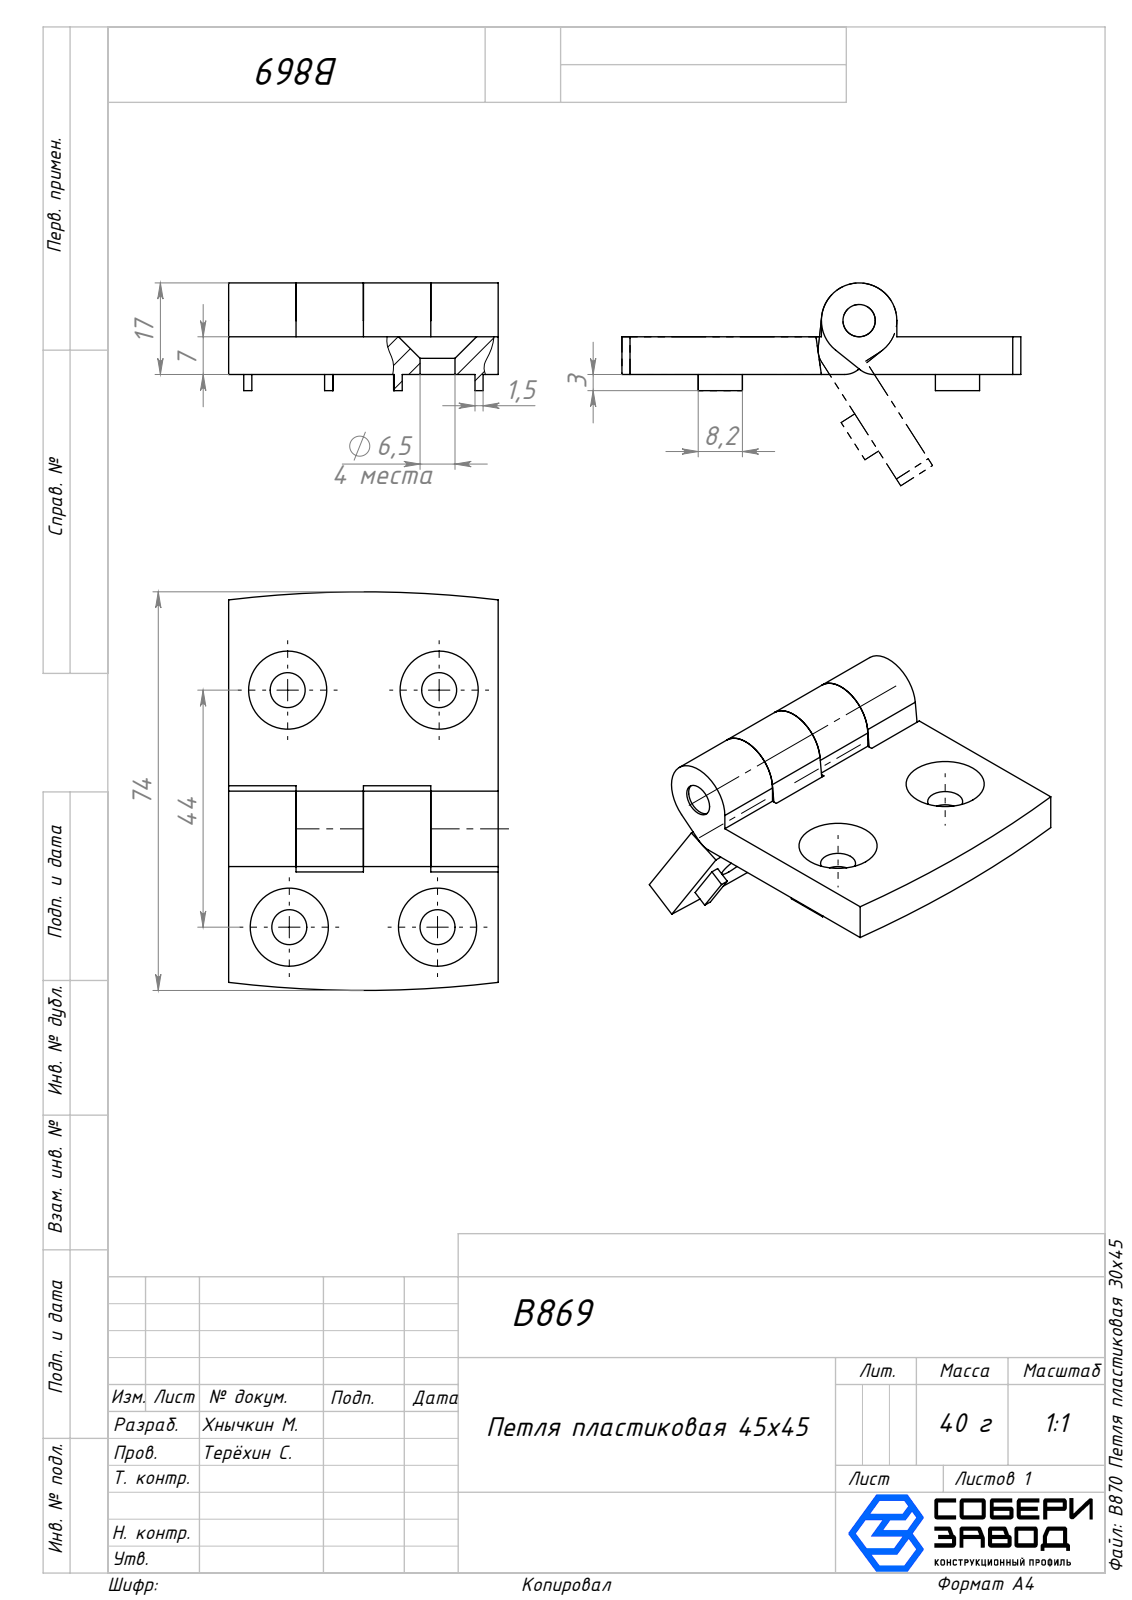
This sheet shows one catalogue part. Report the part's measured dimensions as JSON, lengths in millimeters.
{"part_name": "B870 Петля пластиковая 30х45; Петля 30_00; Петля 45_00; Палец_00", "step_written_by": "SolidWorks 2025 (AUTOMOTIVE_DESIGN)", "units": "millimeters", "bodies": {"solids": 3, "faces": 108, "planar": 68, "cylindrical": 32, "other": 8}, "overall_size": [51, 50, 41.28], "volume_mm3": 28233, "surface_area_mm2": 13732, "round_holes": [[6.5, 4], [6, 1]], "round_bosses_or_shafts": [[14, 1]], "partial_cylinders_radius": [[4, 2], [209.08, 2]], "face_to_face_distances": [7, 12.5, 25, 37.5, 50, 1.5, 8.2, 2.8, 4.3, 45.7], "hole_center_spacings": [27.5, 28.1]}
